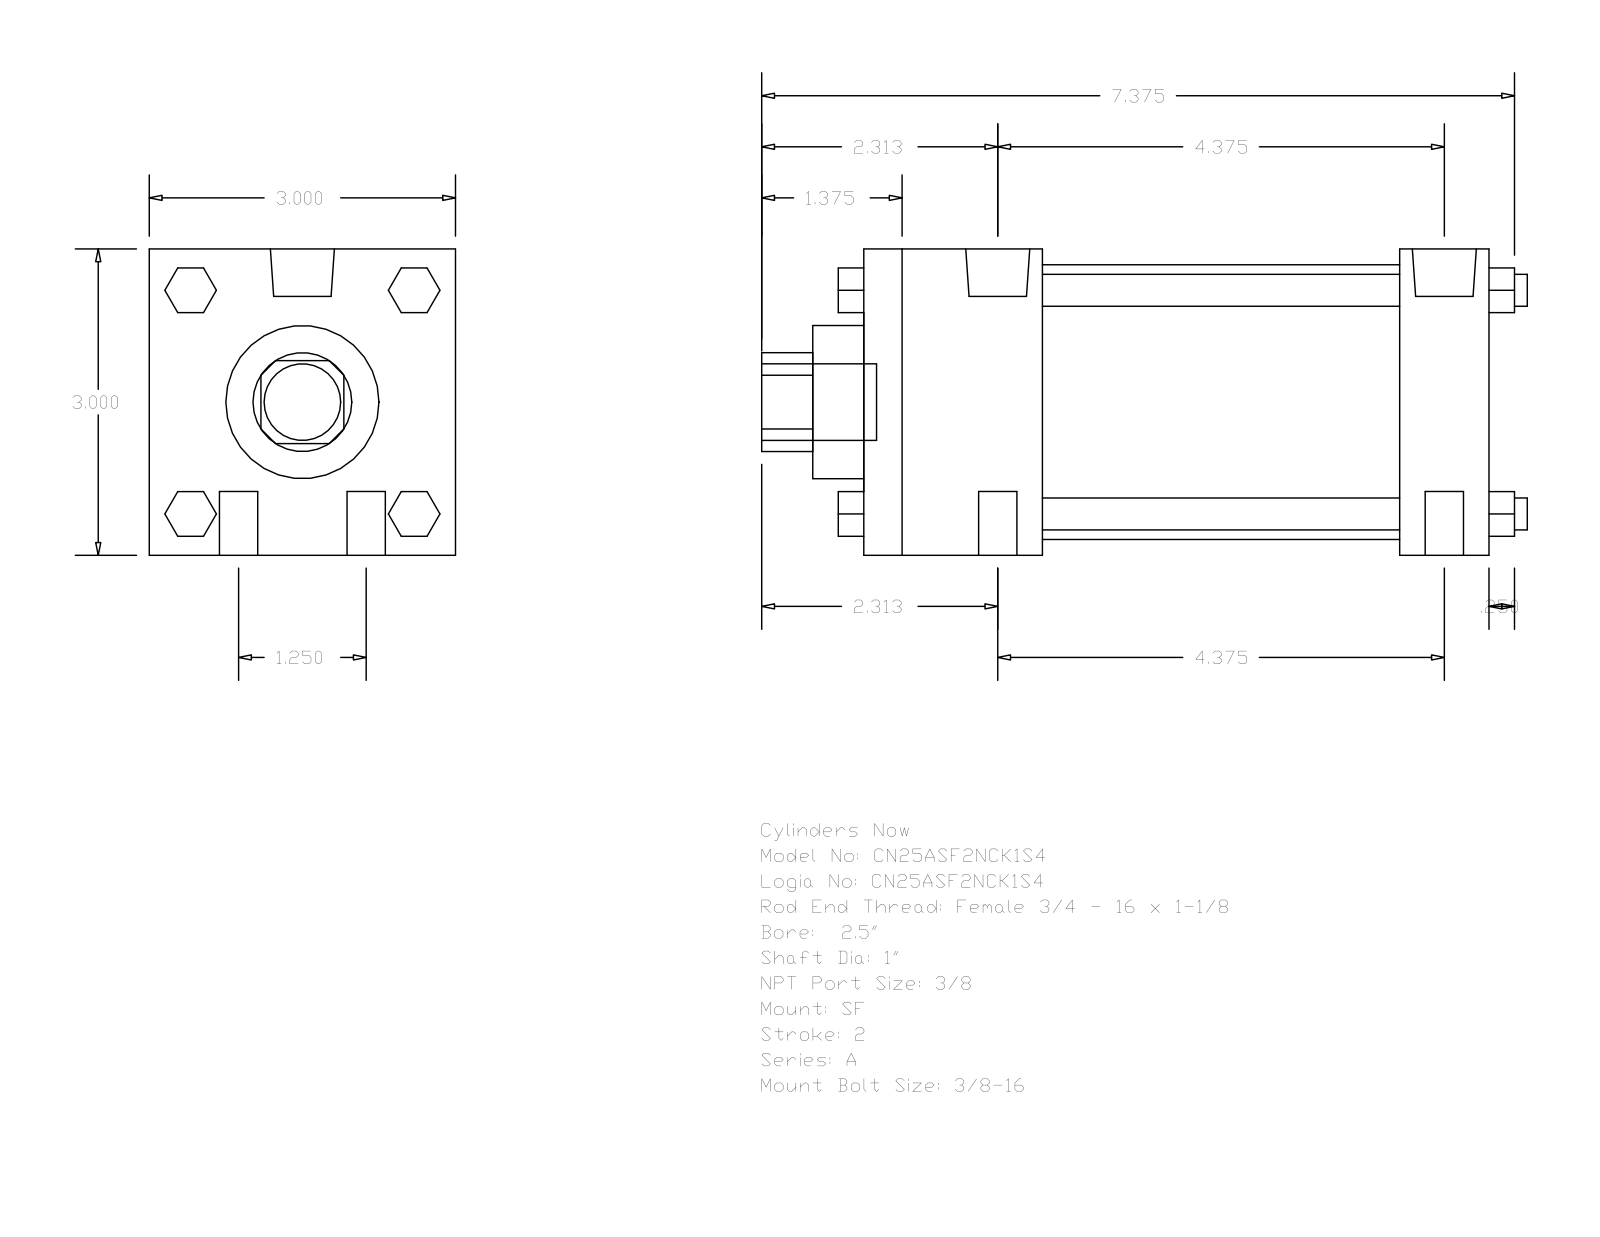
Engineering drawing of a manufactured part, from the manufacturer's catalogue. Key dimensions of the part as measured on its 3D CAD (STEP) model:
Part name (STEP PRODUCT): A_SF__0250_1
STEP written by: GSSL Pune (CONFIG_CONTROL_DESIGN)
Units: millimetres
Bodies: 0 solids, 124 faces (94 planar, 30 cylindrical, 0 other)
Overall size (bounding box): 190.5 × 76.2 × 76.2
Round holes (diameter × count): ⌀25.4 ×1, ⌀38.1 ×1, ⌀68.33 ×1
Round bosses / shafts (diameter × count): ⌀9.53 ×4, ⌀7.94 ×4, ⌀15.93 ×2, ⌀5.56 ×2, ⌀19.05 ×1
Partial cylindrical surfaces — rounded edges, fillets, slot ends (radius × count): R12.29 ×1
Main face-to-face distances: 76.2, 155.57, 133.35, 22.22, 44.45, 88.9, 111.12, 12.7, 168.27, 6.35
